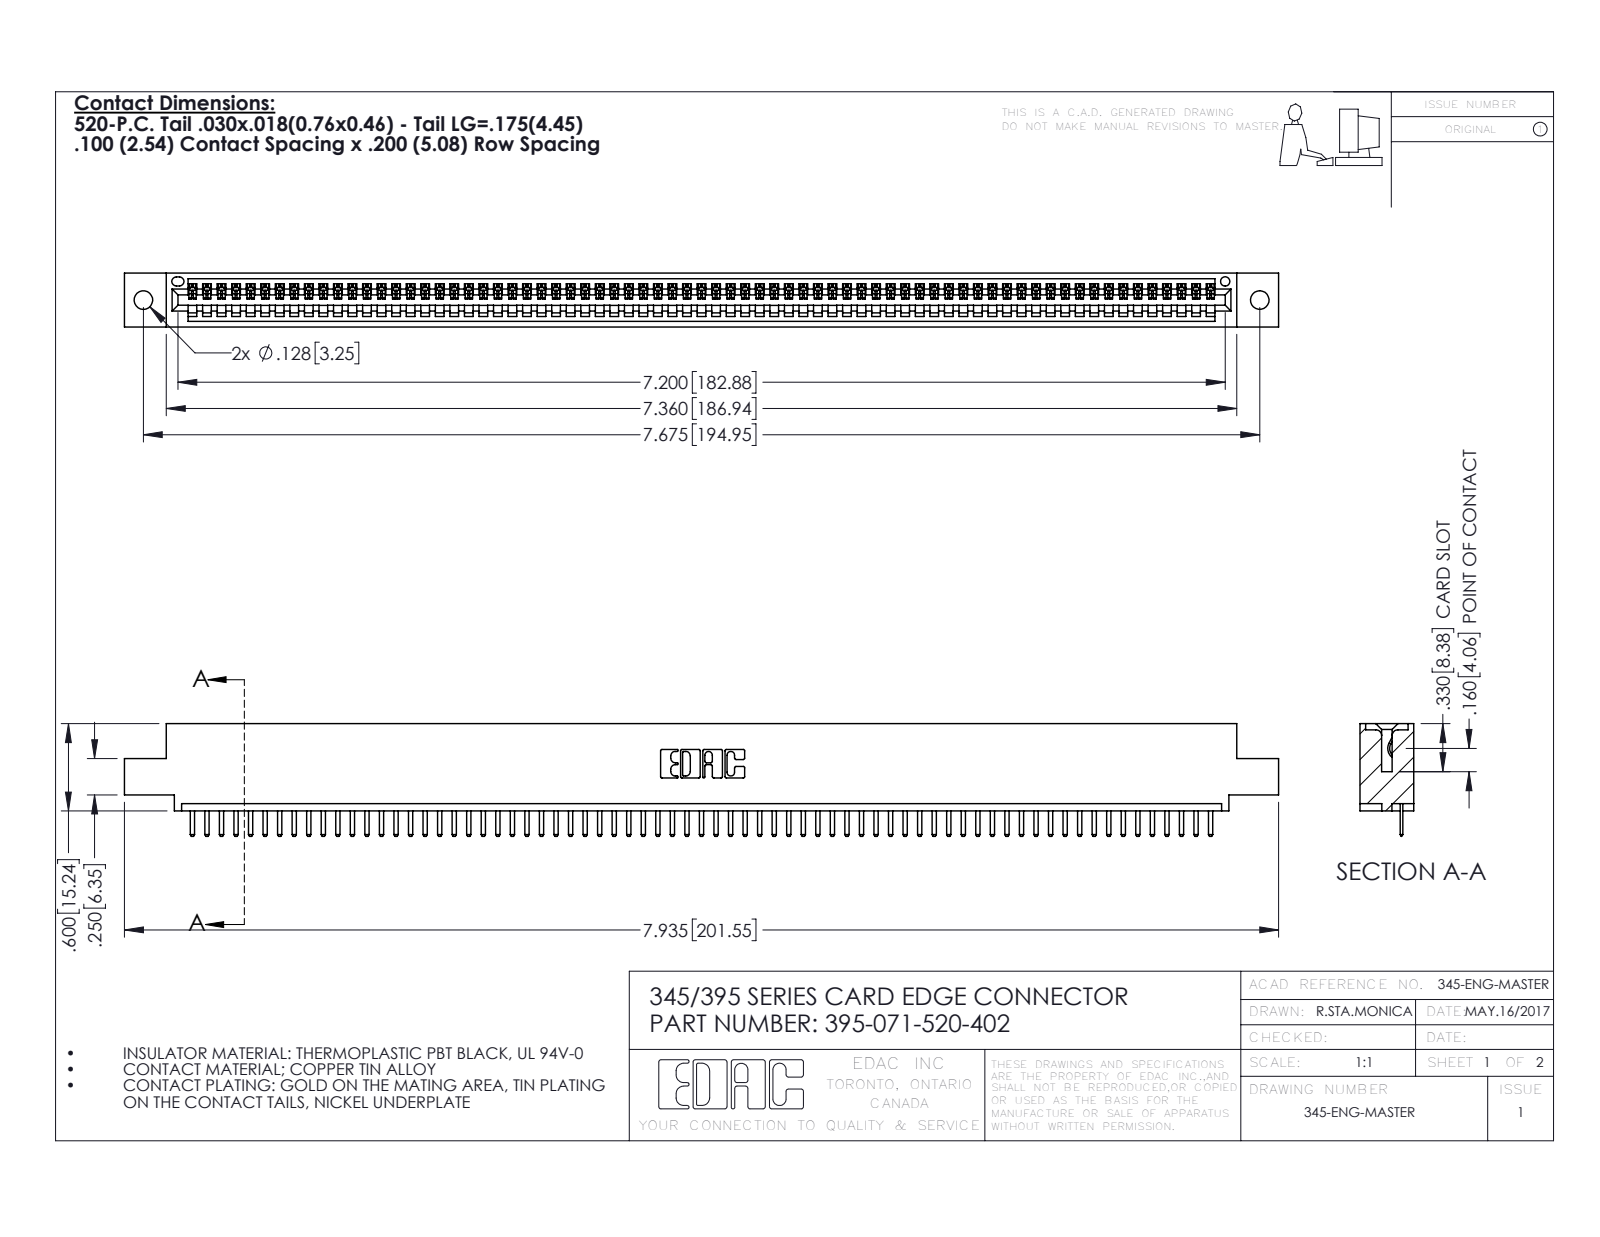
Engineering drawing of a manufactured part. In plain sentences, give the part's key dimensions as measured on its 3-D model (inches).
The part is named "345-292-001_345-293-120; 395-071-520-402; 345 Part_0.110 Offset - 0.128 Dia". Its 3-D file was written by "SolidWorks 2016 (CONFIG_CONTROL_DESIGN)". It is 72 solids with 4532 faces: 3066 planar, 1466 cylindrical and 0 other. Overall it measures 7.935 by 0.775 by 0.37 inches. Its volume is 1.164 cubic inches and its surface area 38.56 square inches. Round holes: 2 of diameter 0.128, 1 of diameter 0.064. Partial cylindrical surfaces (rounded edges, fillets, slot ends): 144 of radius 0.01, 142 of radius 0.006, 22 of radius 0.01, 6 of radius 0.007, 6 of radius 0.031, 3 of radius 0.026, 2 of radius 0.031, 2 of radius 0.04. The main face-to-face distances are 0.298, 0.072, 0.37, 0.2, 0.098, 0.272, 0.025, 0.225, 0.072, 0.149. The hole center spacings are 0.27, 7.439, 7.675.
